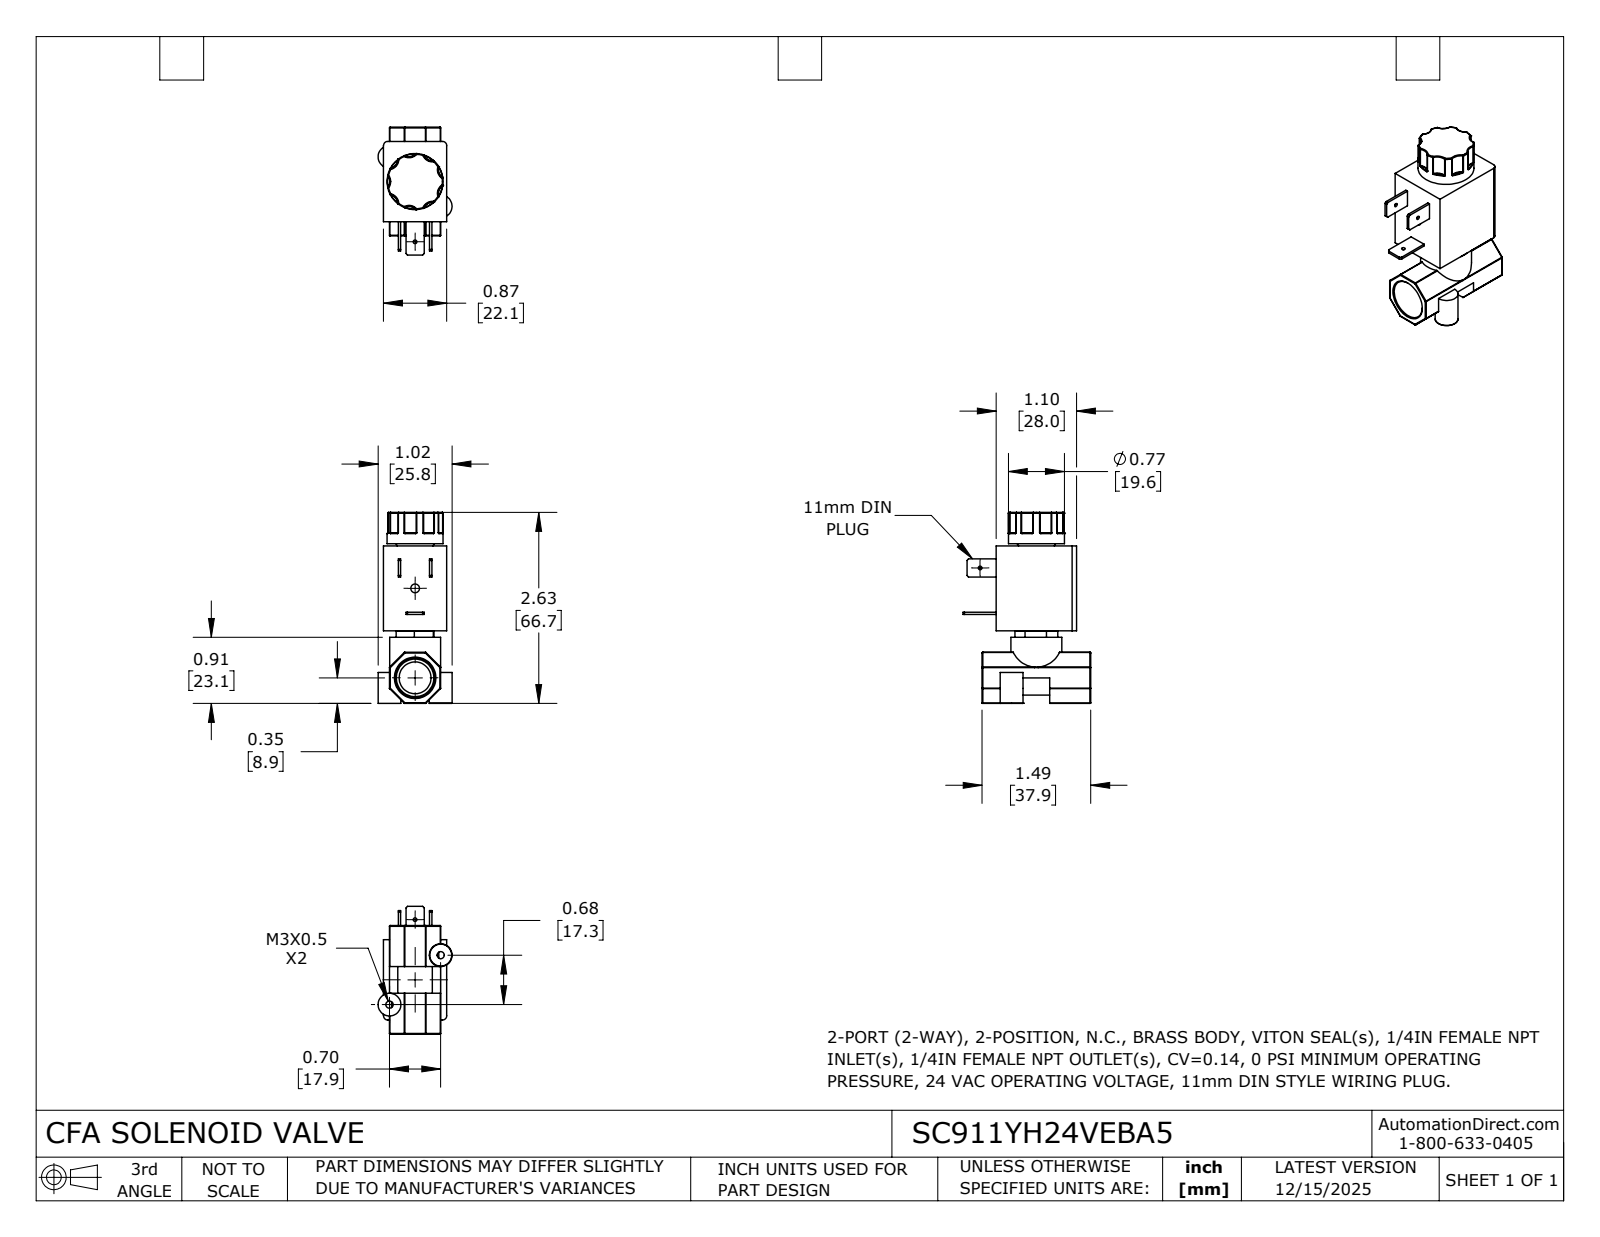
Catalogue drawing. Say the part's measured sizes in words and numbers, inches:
The part is named "SC911YH24VEBA5". Its 3-D file was written by "SolidWorks 2024 (CONFIG_CONTROL_DESIGN)". It is 1 solid with 314 faces: 74 planar, 91 cylindrical and 149 other. Overall it measures 2.625 by 1.757 by 1.017 inches. Its volume is 1.798 cubic inches and its surface area 16.13 square inches. Round holes: 2 of diameter 0.05, 2 of diameter 0.1, 1 of diameter 0.12, 1 of diameter 0.438. Round bosses or shafts: 2 of diameter 0.313, 1 of diameter 0.77, 1 of diameter 0.7. Partial cylindrical surfaces (rounded edges, fillets, slot ends): 42 of radius 0.01, 7 of radius 0.133, 2 of radius 0.06, 2 of radius 0.132, 1 of radius 0.237, 1 of radius 0.325. The main face-to-face distances are 0.87, 0.704, 1.104, 1.167, 0.083, 0.787, 0.46, 0.998, 2.165, 2.625. The hole center spacings are 0.602, 0.979, 1.22, 1.23.
